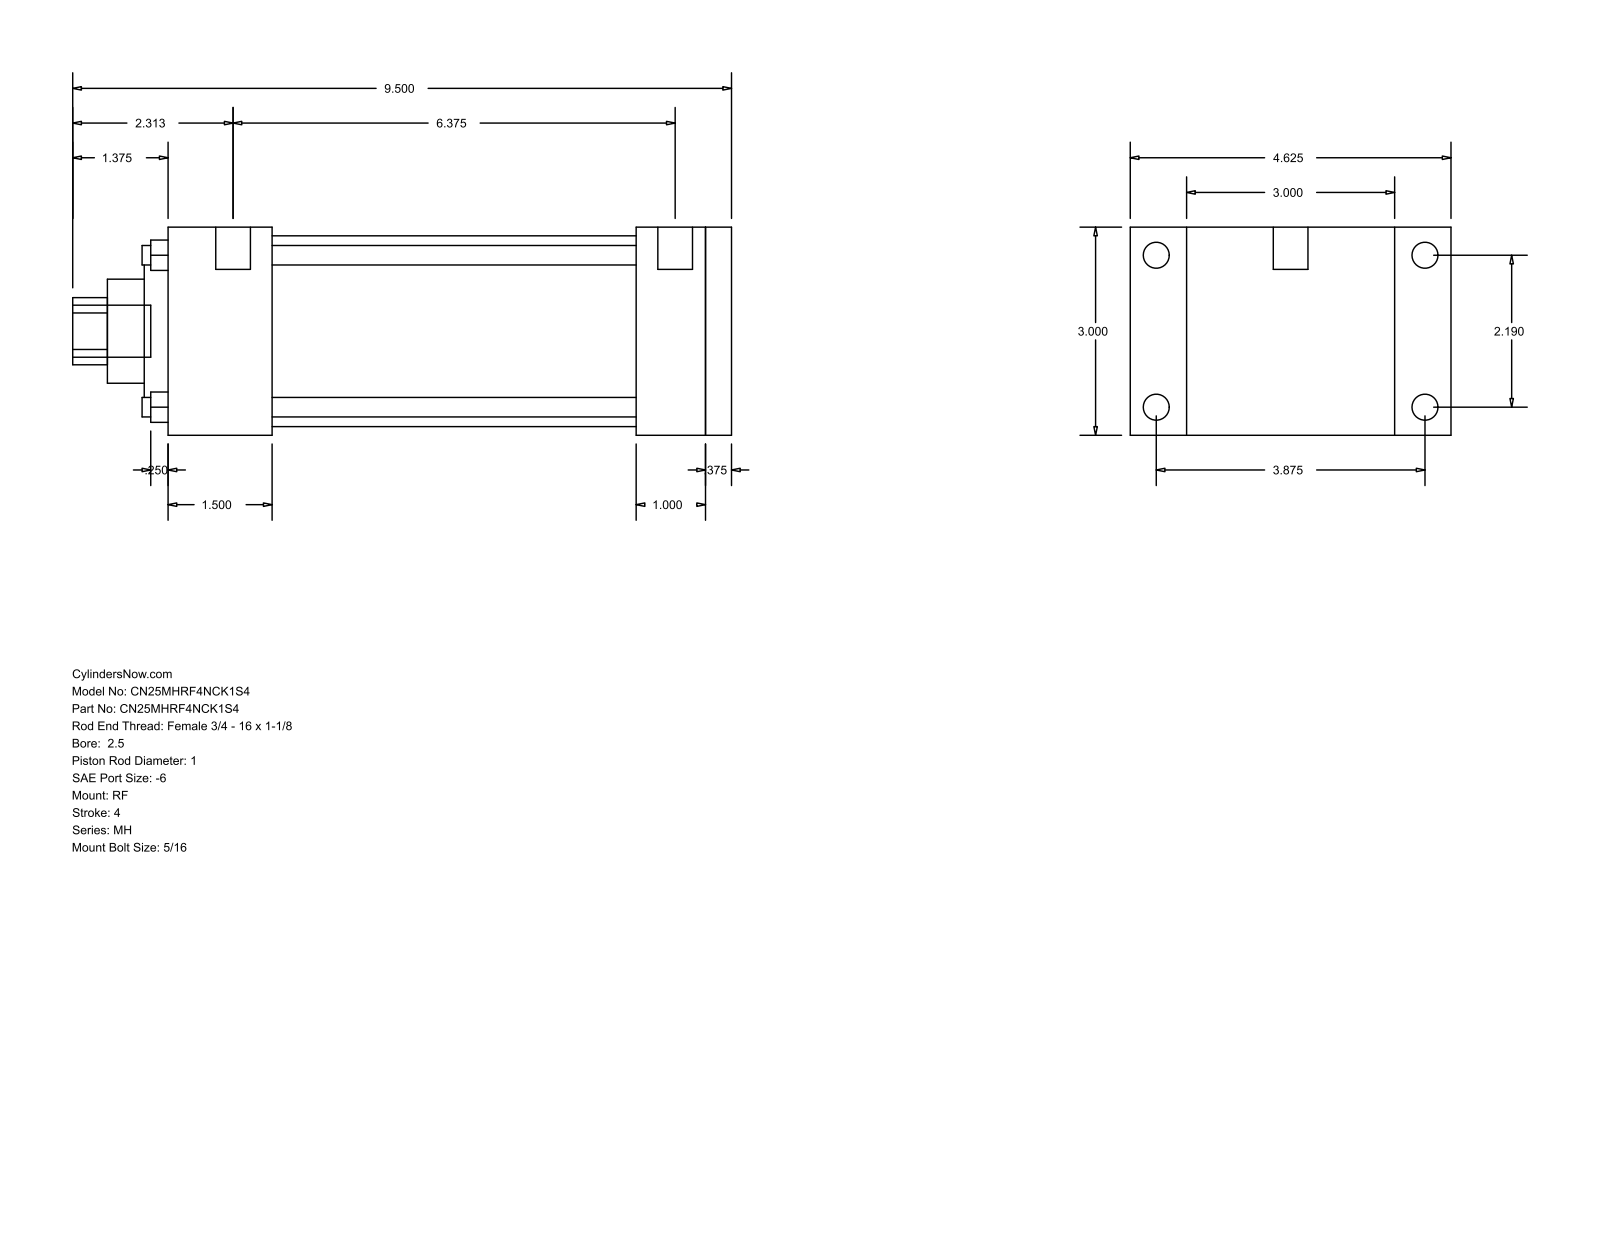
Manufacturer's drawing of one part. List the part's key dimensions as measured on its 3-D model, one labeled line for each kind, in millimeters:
Part name (STEP PRODUCT): MH_RF__0250_1
STEP written by: GSSL Pune (CONFIG_CONTROL_DESIGN)
Units: millimetres
Bodies: 0 solids, 94 faces (65 planar, 29 cylindrical, 0 other)
Overall size (bounding box): 241.3 × 117.47 × 76.2
Round holes (diameter × count): ⌀7.14 ×4, ⌀25.4 ×1, ⌀38.1 ×1, ⌀60.33 ×1, ⌀69.85 ×1
Round bosses / shafts (diameter × count): ⌀9.53 ×4, ⌀5.56 ×4, ⌀12.7 ×2, ⌀19.05 ×1
Partial cylindrical surfaces — rounded edges, fillets, slot ends (radius × count): R12.29 ×1
Main face-to-face distances: 76.2, 9.52, 206.38, 196.86, 25.4, 34.92, 171.46, 38.11, 133.35, 158.75
Hole centre spacings: 39.33, 55.62, 78.66
